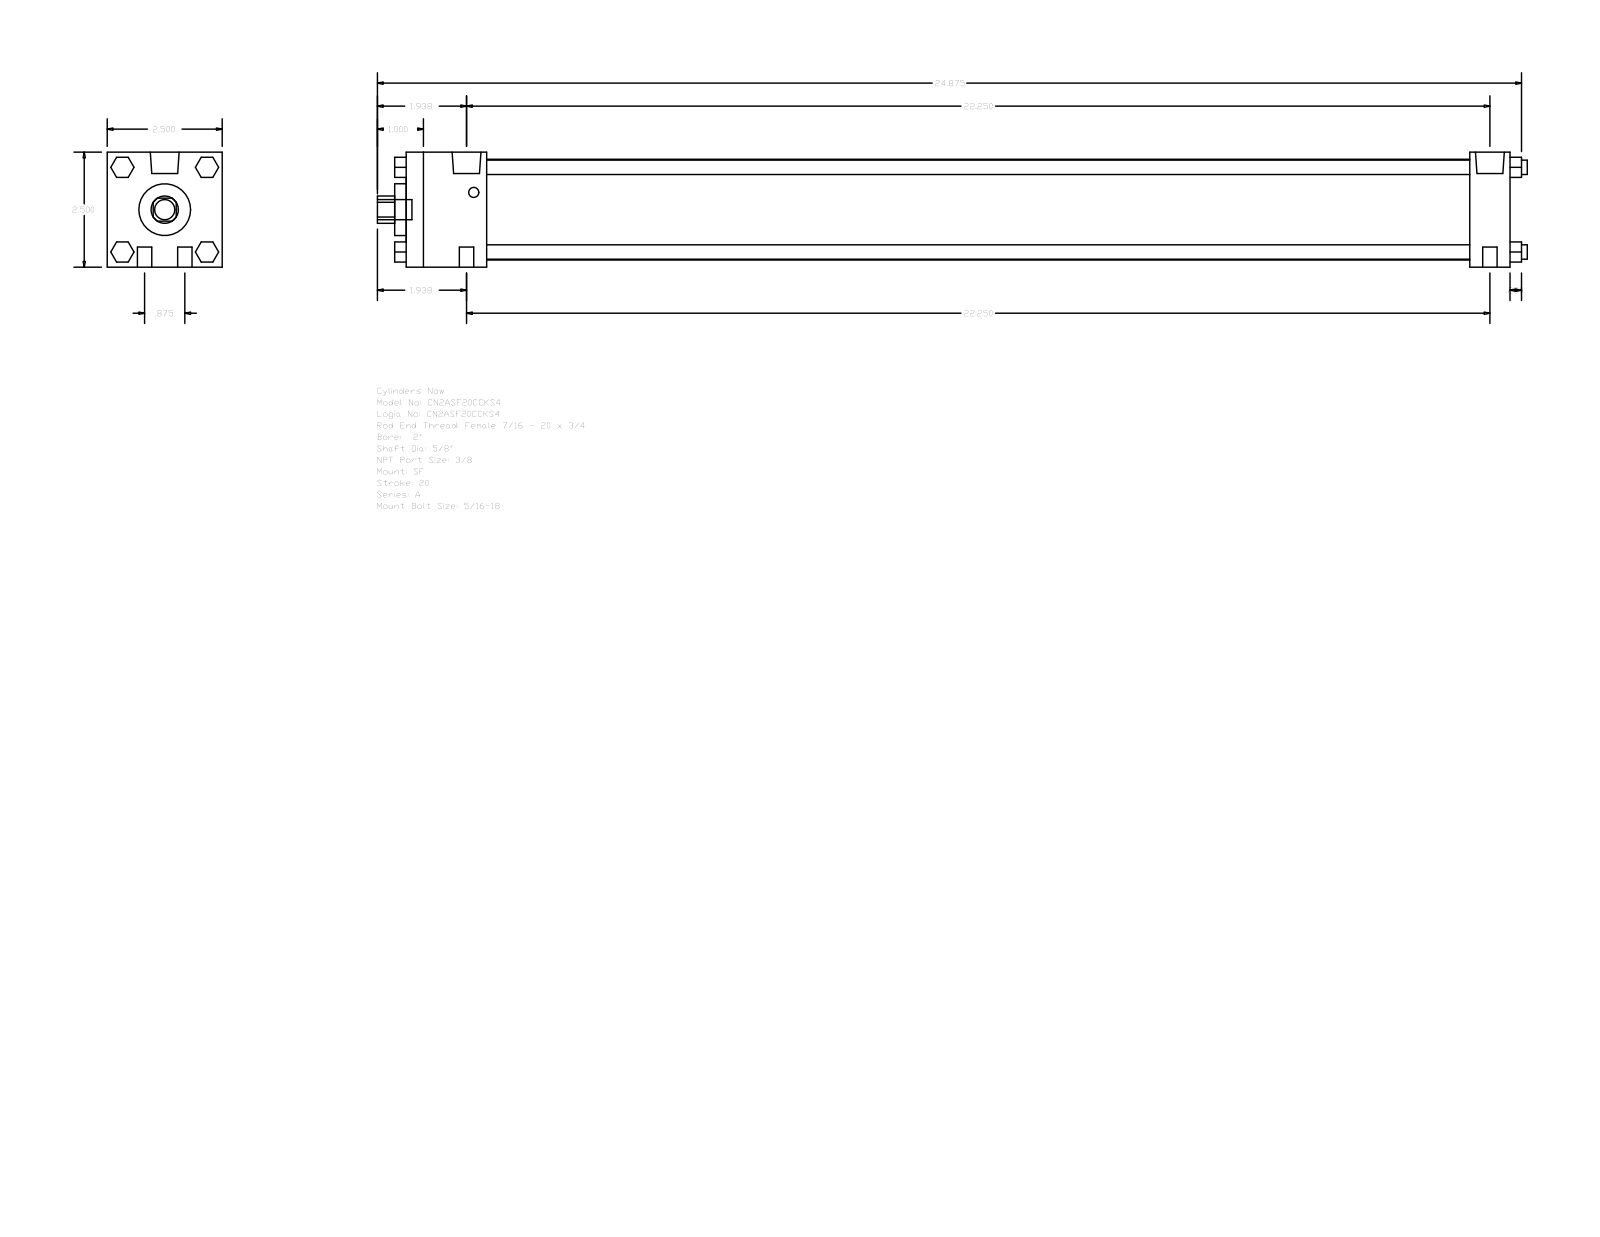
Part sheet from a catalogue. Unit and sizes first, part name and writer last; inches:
Units: inches
Overall size (bounding box): 25 × 2.5 × 2.5
Round holes (diameter × count): ⌀0.625 ×1, ⌀1.125 ×1, ⌀2.19 ×1
Round bosses / shafts (diameter × count): ⌀0.313 ×8, ⌀0.627 ×2, ⌀0.219 ×2, ⌀0.437 ×1
Partial cylindrical surfaces — rounded edges, fillets, slot ends (radius × count): R0.297 ×1
Main face-to-face distances: 2.5, 24, 23.125, 0.875, 1.75, 21.375, 22.25, 24.25, 0.25, 2
Bodies: 0 solids, 124 faces (94 planar, 30 cylindrical, 0 other)
Part name (STEP PRODUCT): A_SF__0200_0.625
STEP written by: GSSL Pune (CONFIG_CONTROL_DESIGN)
